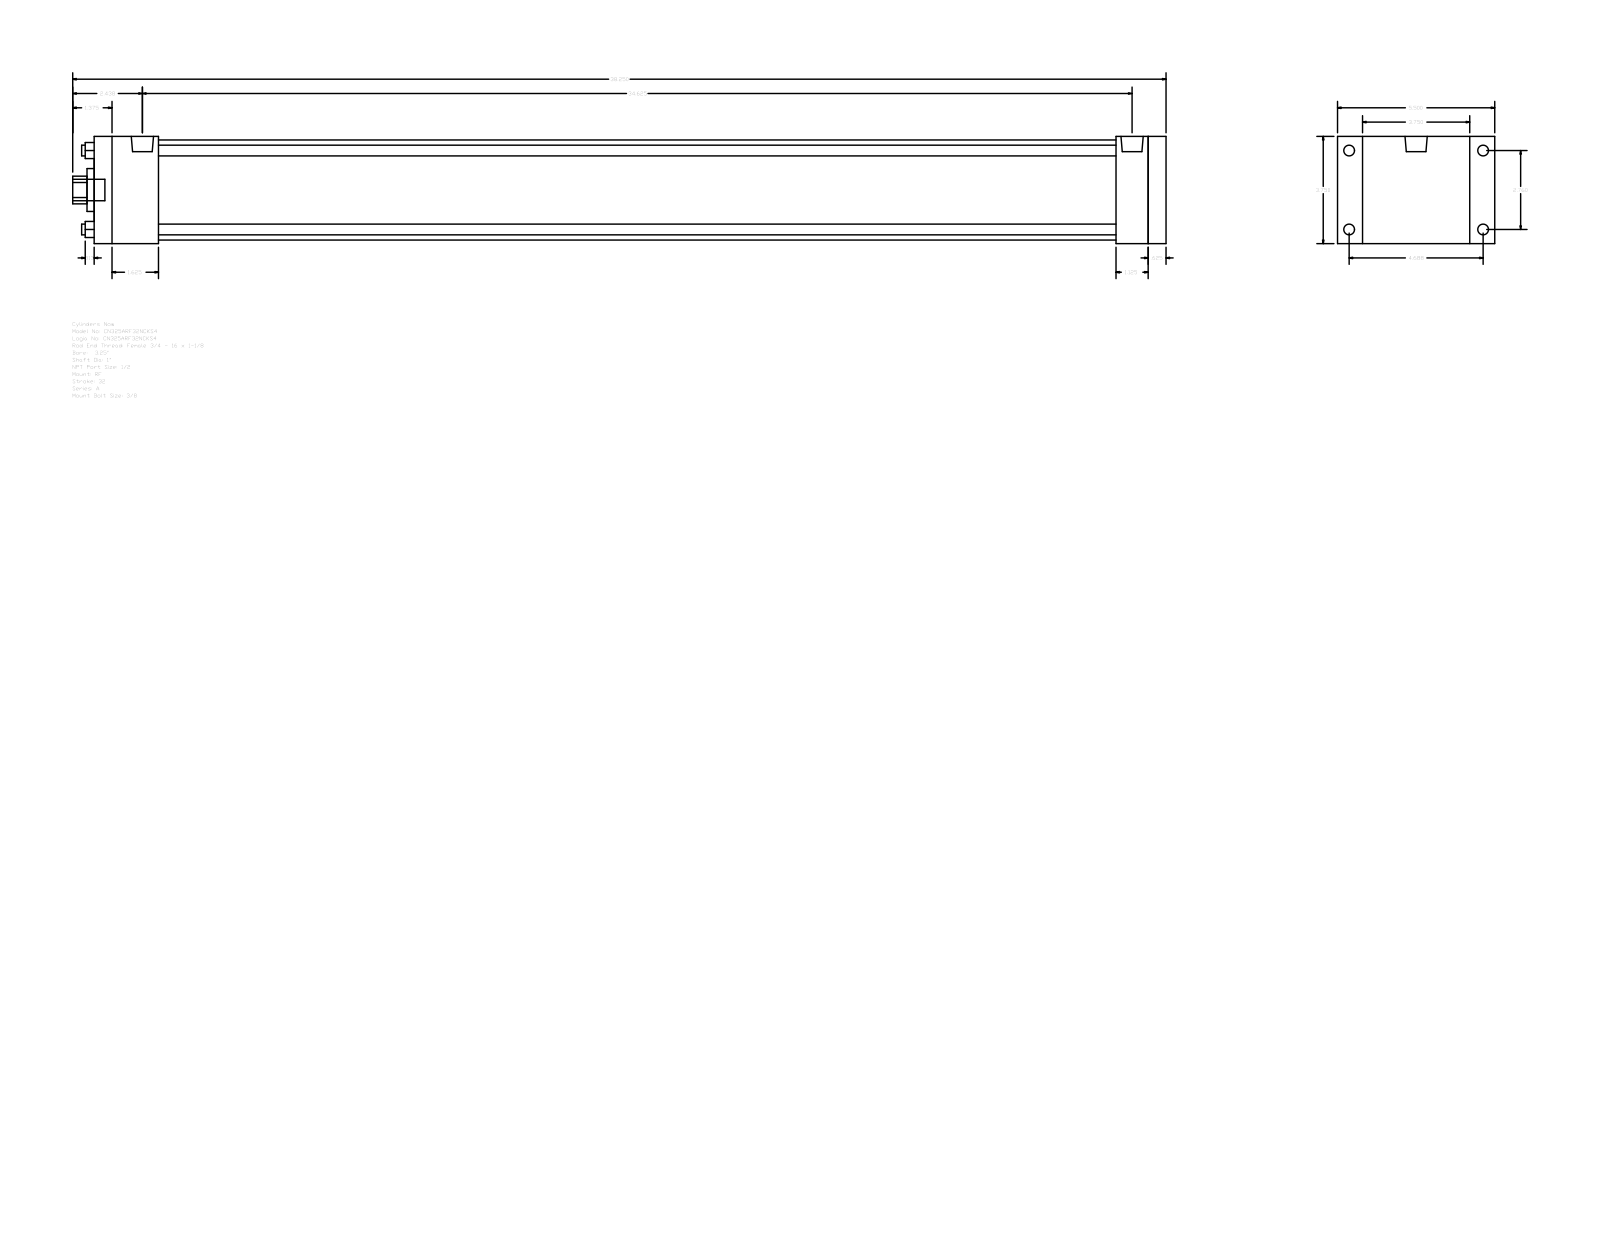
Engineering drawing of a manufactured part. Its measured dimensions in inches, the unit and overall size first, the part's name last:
Units: inches
Overall size (bounding box): 38.25 × 5.5 × 3.75
Round holes (diameter × count): ⌀0.375 ×4, ⌀1 ×1, ⌀1.5 ×1, ⌀3.5 ×1
Round bosses / shafts (diameter × count): ⌀0.375 ×4, ⌀0.344 ×4, ⌀0.778 ×2, ⌀0.75 ×1
Partial cylindrical surfaces — rounded edges, fillets, slot ends (radius × count): R0.484 ×1
Main face-to-face distances: 3.75, 37.5, 36.875, 0.625, 0.875, 4.625, 1.125, 35.75, 1.75, 2.25
Hole centre spacings: 1.952, 2.76, 3.903
Bodies: 0 solids, 92 faces (64 planar, 28 cylindrical, 0 other)
Part name (STEP PRODUCT): A_RF__0325_1
STEP written by: GSSL Pune (CONFIG_CONTROL_DESIGN)
